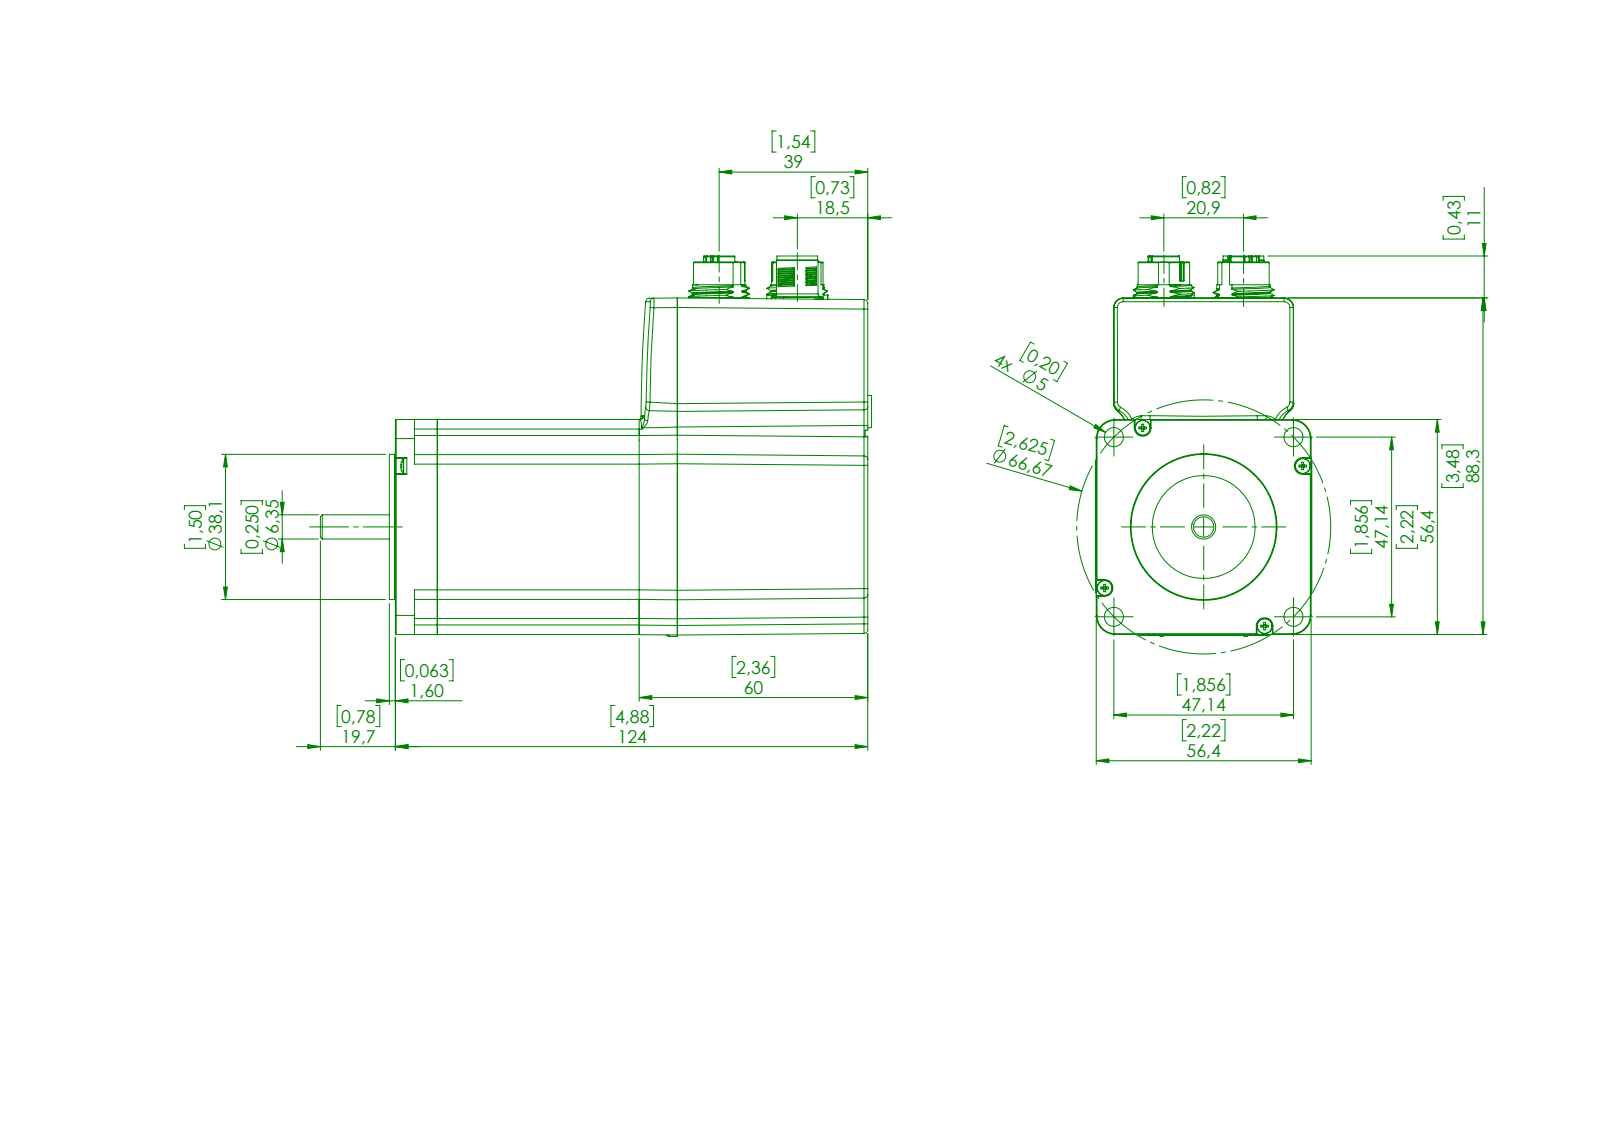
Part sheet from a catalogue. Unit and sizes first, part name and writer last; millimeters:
Units: millimetres
Overall size (bounding box): 144.7 × 99.83 × 56.67
Round holes (diameter × count): ⌀1 ×31, ⌀2 ×4, ⌀2.5 ×4, ⌀5 ×4, ⌀15.5 ×4, ⌀18.5 ×4, ⌀12.2 ×3, ⌀1.52 ×2, ⌀2.2 ×2, ⌀8.6 ×2, ⌀11.13 ×2, ⌀14.6 ×2
Round bosses / shafts (diameter × count): ⌀1.1 ×17, ⌀0.6 ×17, ⌀1.6 ×13, ⌀1 ×7, ⌀13.25 ×4, ⌀13.5 ×3, ⌀4 ×3, ⌀0.22 ×3
Partial cylindrical surfaces — rounded edges, fillets, slot ends (radius × count): R0.2 ×63, R0.1 ×32, R2.5 ×29, R5 ×18, R1 ×16, R0.8 ×12, R0.15 ×10, R1.6 ×9
Main face-to-face distances: 10, 63, 53, 56.4, 113, 50, 60, 4.75, 49.3, 0.7
Hole centre spacings: 3.54, 1.63, 2.5, 3.25, 39.89, 1.85, 4.94, 1.64
Volume: 449 782 mm³ · Surface area: 79 058 mm²
Bodies: 16 solids, 2595 faces (959 planar, 765 cylindrical, 871 other)
Part name (STEP PRODUCT): Stator_MIS23X; Housing_MIS23X_Top_R8_S; M12_17P_FEMALE; Motor_end_cover_MIS23X_R3_S (+8 more)
STEP written by: SolidWorks 2017 (CONFIG_CONTROL_DESIGN)
